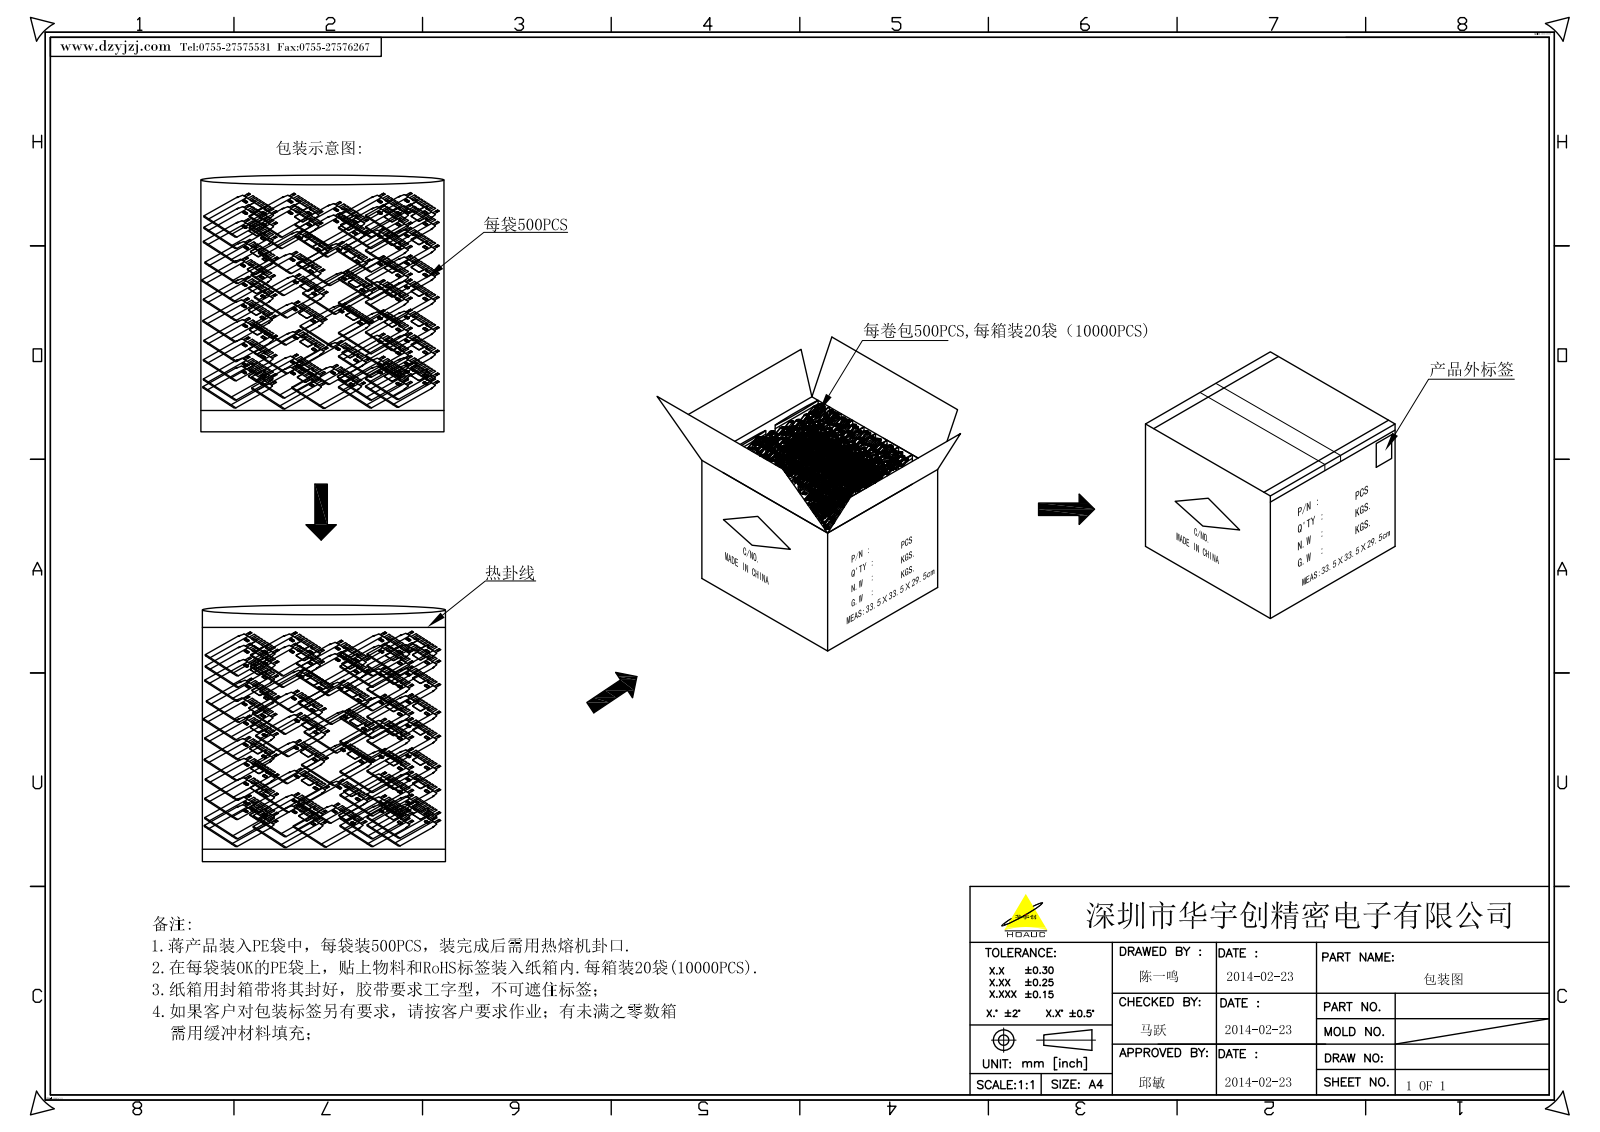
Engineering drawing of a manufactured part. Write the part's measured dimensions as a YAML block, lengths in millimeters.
part_name: "TANPIAN-PLASTIC_1_2__2_30_1_1_1"
step_written_by: "CREO PARAMETRIC BY PTC INC, 2022073 (AUTOMOTIVE_DESIGN)"
units: millimeters
bodies: {solids: 1, faces: 661, planar: 446, cylindrical: 209, other: 6}
overall_size: [13.01, 8.25, 2.42]
volume: 171
surface_area: 626
partial_cylinders:
  - {radius: 0.15, count: 39}
  - {radius: 0.2, count: 10}
  - {radius: 0.3, count: 8}
  - {radius: 1.05, count: 8}
  - {radius: 0.13, count: 6}
  - {radius: 0.25, count: 6}
  - {radius: 0.5, count: 4}
  - {radius: 1, count: 4}
face_to_face_distances: [2.25, 2.23, 2.4, 0.64, 0.8, 1.44, 0.81, 1.61, 0.79, 0.66]
